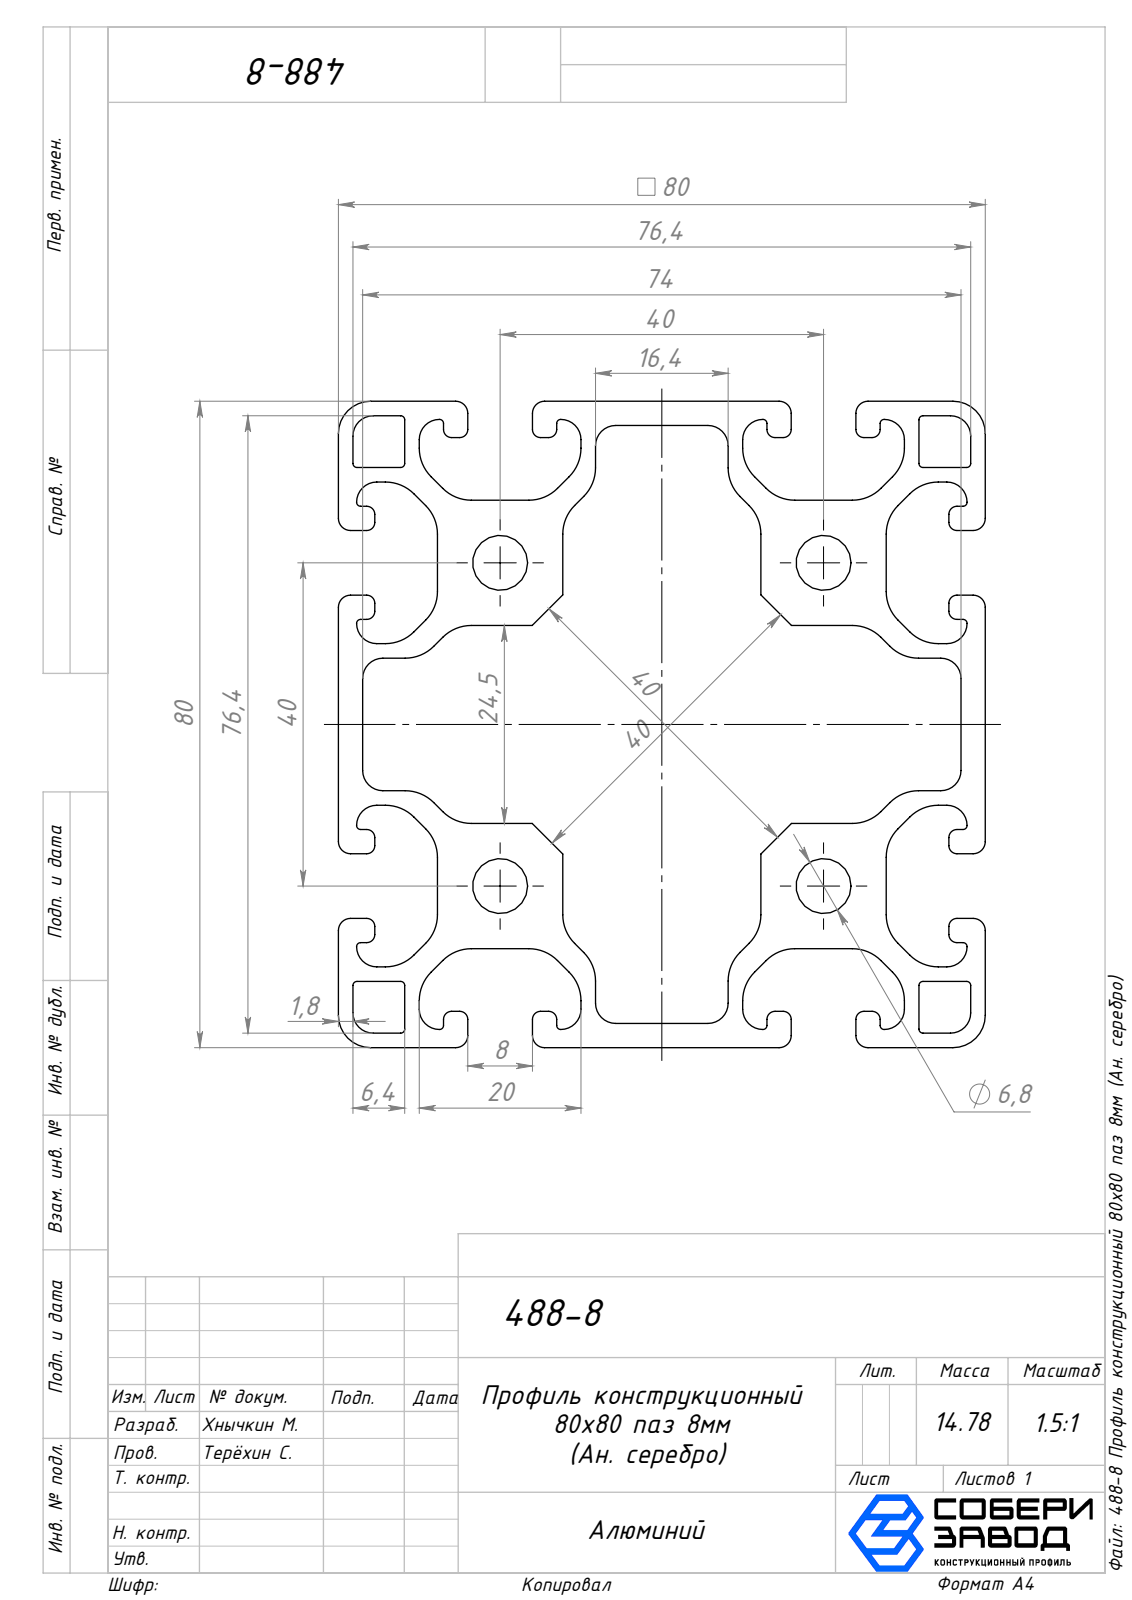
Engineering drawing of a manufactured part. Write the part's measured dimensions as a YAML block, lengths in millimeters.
part_name: "V053-8951"
step_written_by: "SolidWorks 2025 (AUTOMOTIVE_DESIGN)"
units: millimeters
bodies: {solids: 1, faces: 314, planar: 150, cylindrical: 164, other: 0}
overall_size: [1000, 80, 80]
volume: 1893000
surface_area: 1119000
round_holes:
  - {diameter: 6.8, count: 4}
partial_cylinders:
  - {radius: 5, count: 48}
  - {radius: 1, count: 32}
  - {radius: 0.5, count: 28}
  - {radius: 2.5, count: 24}
  - {radius: 1.5, count: 16}
  - {radius: 4, count: 8}
face_to_face_distances: [40, 80, 3, 4.05, 19.55, 27.75, 52.25, 67.75, 12.25, 15.5]
hole_center_spacings: [40, 56.57]
